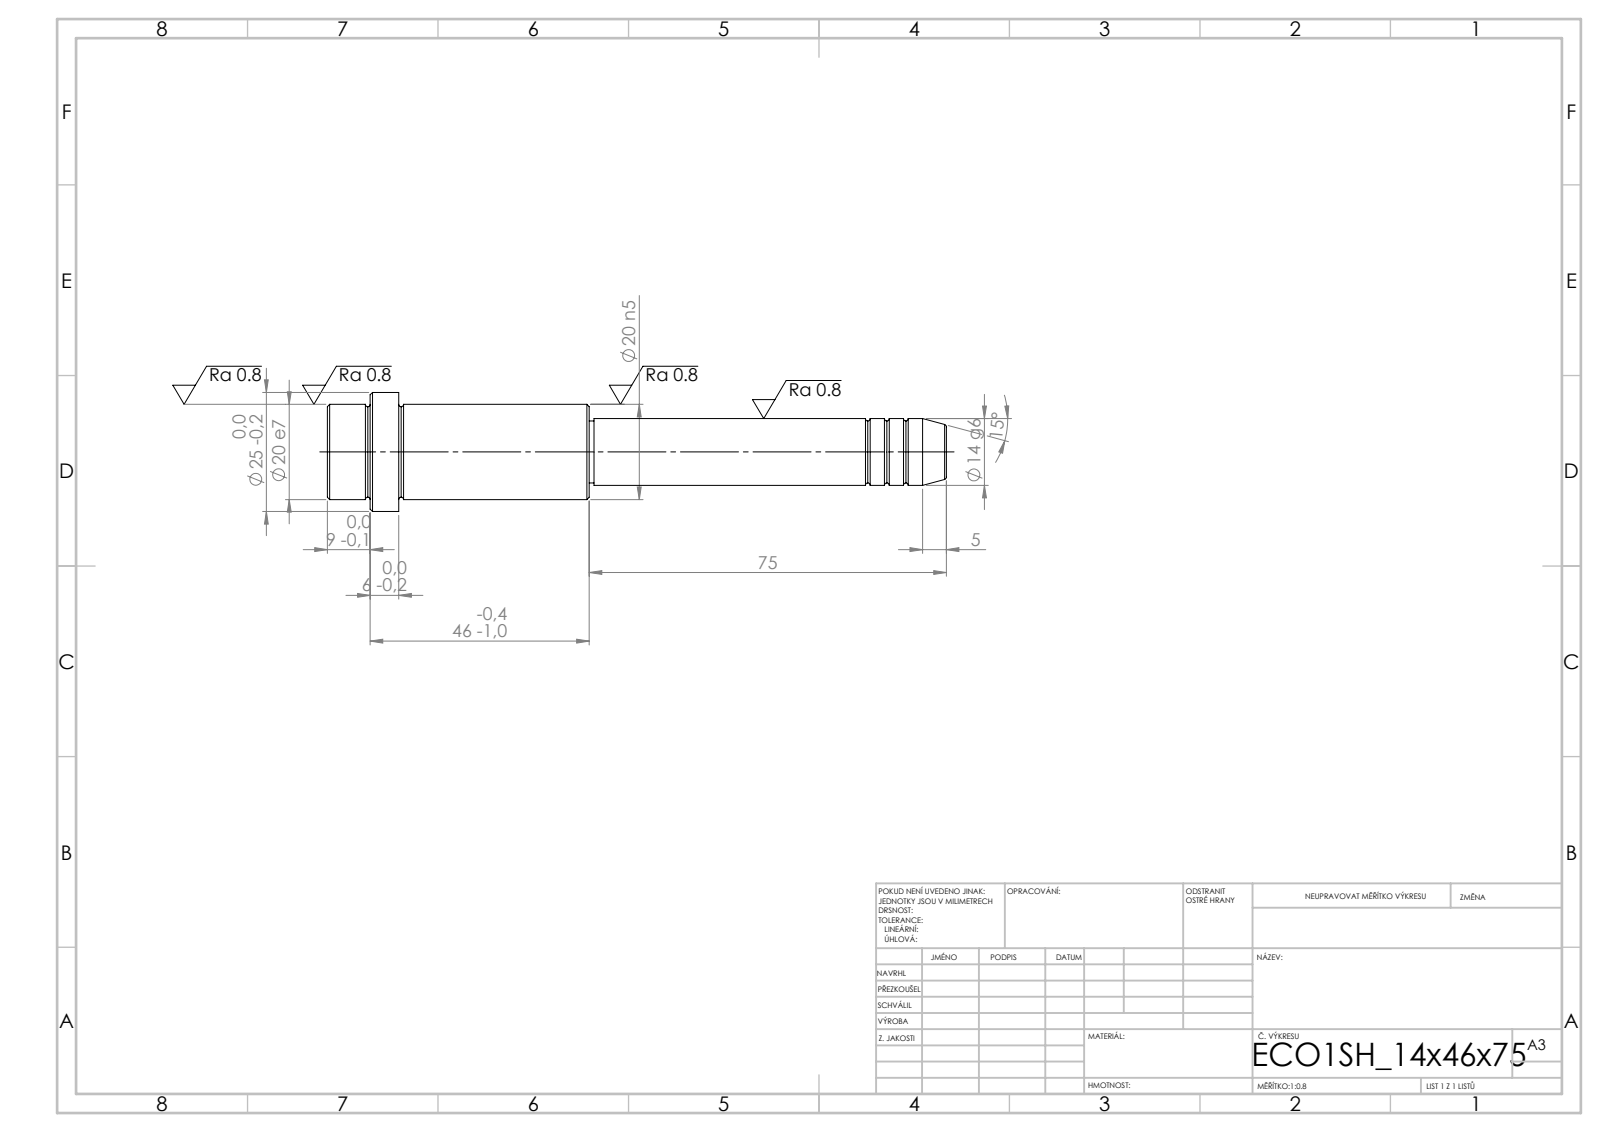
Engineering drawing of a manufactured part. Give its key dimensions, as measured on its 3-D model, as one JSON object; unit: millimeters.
{"step_written_by": "SolidWorks 2019 (CONFIG_CONTROL_DESIGN)", "units": "millimeters", "bodies": {"solids": 1, "faces": 52, "planar": 6, "cylindrical": 16, "other": 30}, "overall_size": [130, 25, 25], "volume_mm3": 29601, "surface_area_mm2": 7869, "round_bosses_or_shafts": [[25, 1], [20, 1], [14, 1], [13, 1]], "face_to_face_distances": [15, 40, 55, 46, 6, 9, 75, 115, 121, 130]}
